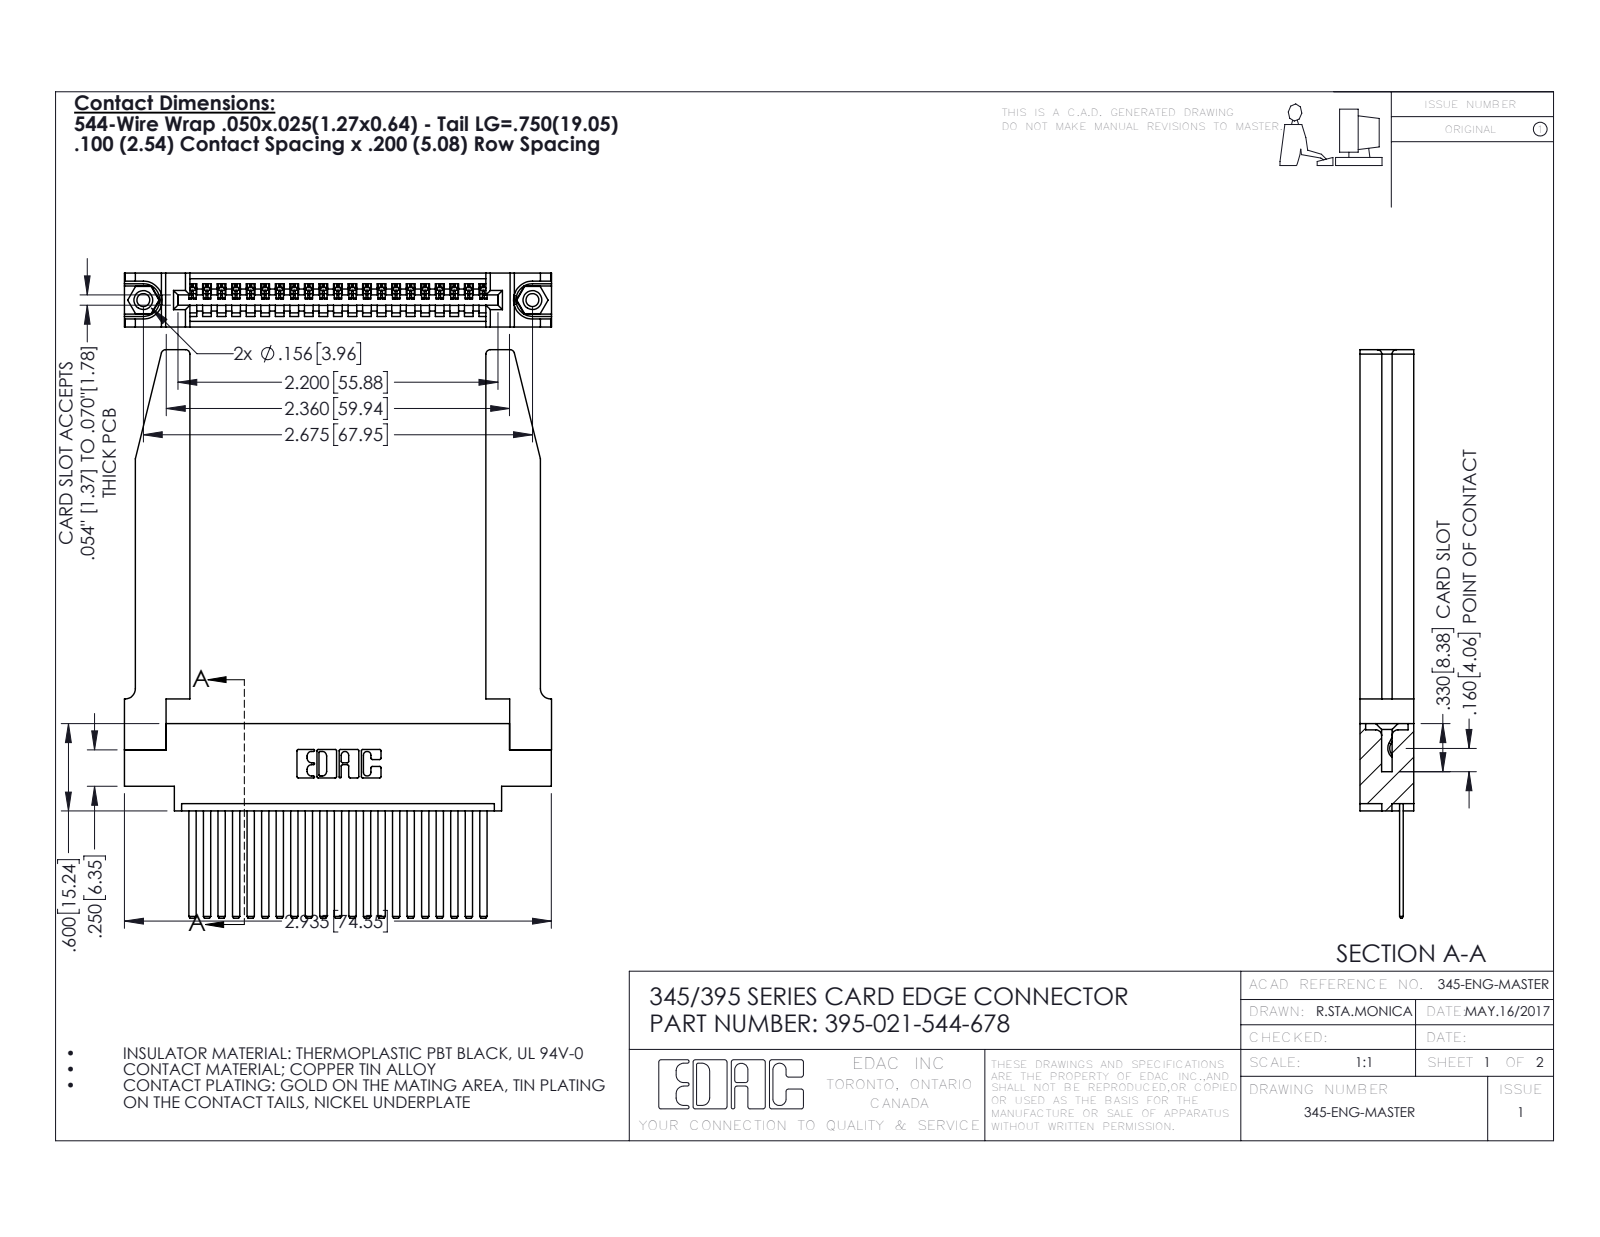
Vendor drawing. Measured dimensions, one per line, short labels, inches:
name: 345-220-078_345-220-078; 395-021-544-678; 345-250-001_345-250-001-102; 345-292-001_345-293-144 (+1 more)
written by: SolidWorks 2016 (CONFIG_CONTROL_DESIGN)
unit: in
bodies: 26 solids, 1456 faces (982 planar, 422 cylindrical, 52 other)
size: 3.907 × 2.936 × 0.37
volume: 0.904 in³; area: 26 in²
holes: 2× ⌀0.089, 2× ⌀0.125, 2× ⌀0.156, 1× ⌀0.064
bosses: 2× ⌀0.155
rounds: 42× R0.006, 22× R0.01, 8× R0.03, 6× R0.007, 6× R0.031, 3× R0.026, 2× R0.031, 2× R0.04
face distances: 0.37, 0.072, 0.298, 0.098, 0.272, 0.025, 0.2, 0.15, 0.148, 0.22
hole spacings: 0.27, 2.441, 2.675
